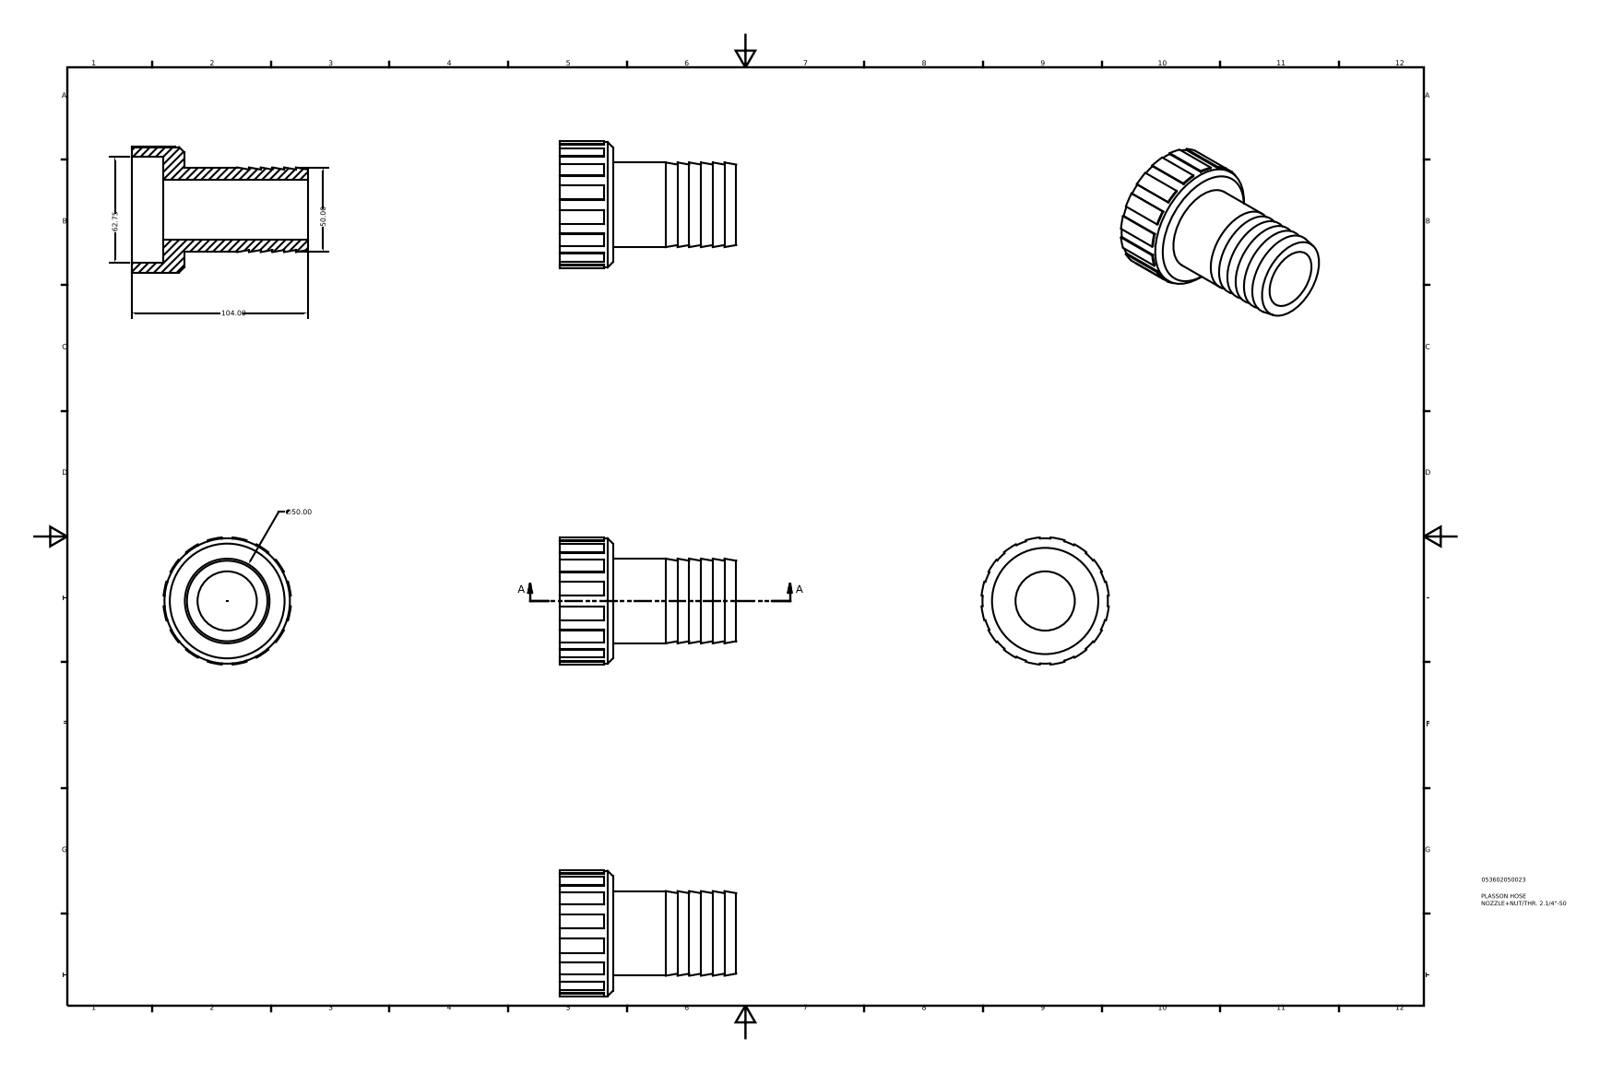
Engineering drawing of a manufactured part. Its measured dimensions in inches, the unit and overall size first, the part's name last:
Units: inches
Overall size (bounding box): 4.094 × 2.954 × 2.954
Round holes (diameter × count): ⌀1.378 ×1, ⌀2.47 ×1
Round bosses / shafts (diameter × count): ⌀2.915 ×1, ⌀1.969 ×1
Partial cylindrical surfaces — rounded edges, fillets, slot ends (radius × count): R1.482 ×1
Main face-to-face distances: 0.491, 0.737, 1.228, 4.094, 3.357, 2.866, 0.546, 0.819, 0.273, 0.273
Volume: 8.209 in³ · Surface area: 61.14 in²
Bodies: 1 solid, 84 faces (57 planar, 20 cylindrical, 7 other)
Part name (STEP PRODUCT): 053602050023
STEP written by: Autodesk Inventor 2015 (AUTOMOTIVE_DESIGN)
